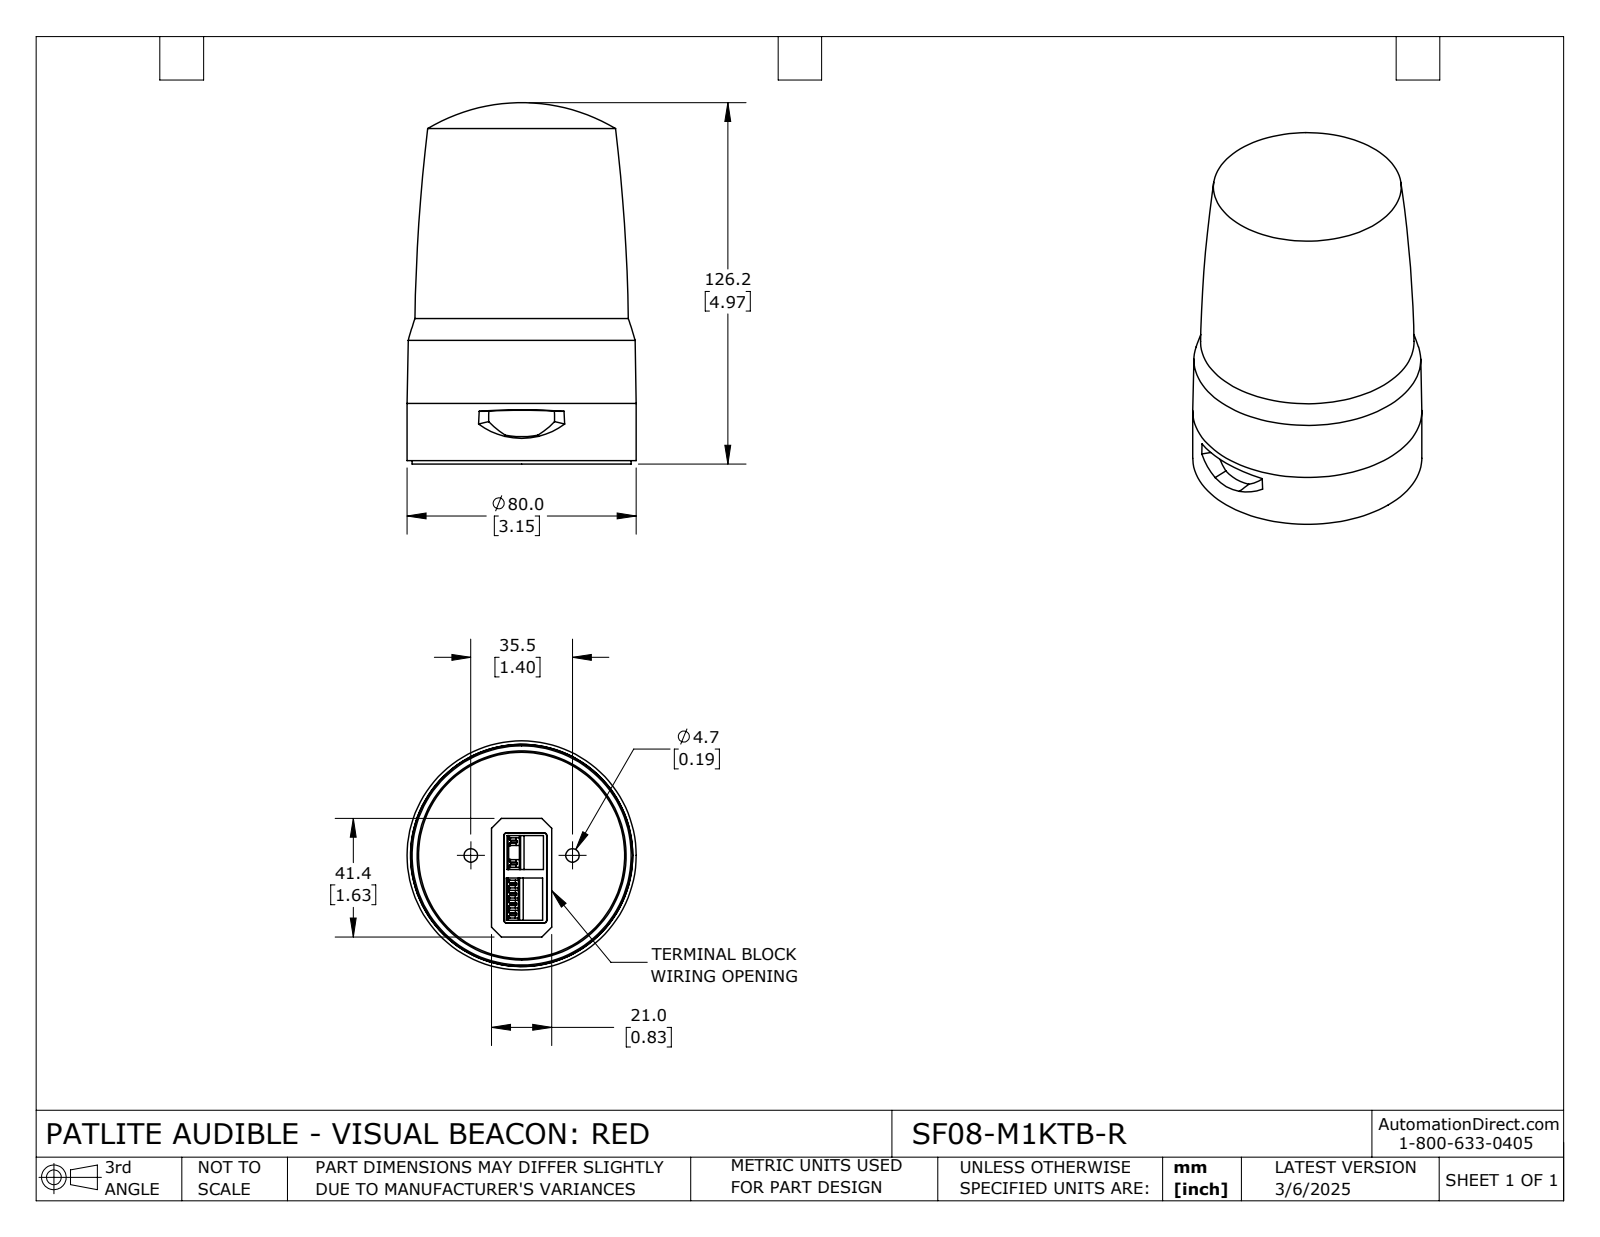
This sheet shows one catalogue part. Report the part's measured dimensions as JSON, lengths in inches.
{"part_name": "SF08-M1KTB-R", "step_written_by": "SolidWorks 2024 (CONFIG_CONTROL_DESIGN)", "units": "inches", "bodies": {"solids": 2, "faces": 262, "planar": 168, "cylindrical": 32, "other": 62}, "overall_size": [4.969, 3.15, 3.15], "volume_in3": 29.79, "surface_area_in2": 84.61, "round_holes": [[0.185, 2], [0.48, 2], [2.874, 1]], "round_bosses_or_shafts": [[3.15, 1], [3.012, 1], [2.937, 1], [2.835, 1]], "partial_cylinders_radius": [[0.039, 4], [0.012, 2], [1.362, 1], [1.378, 1]], "face_to_face_distances": [0.618, 0.248, 0.37, 0.118, 0.201, 0.571, 0.124, 0.242, 0.051, 0.49], "hole_center_spacings": [0.699, 1.398]}
